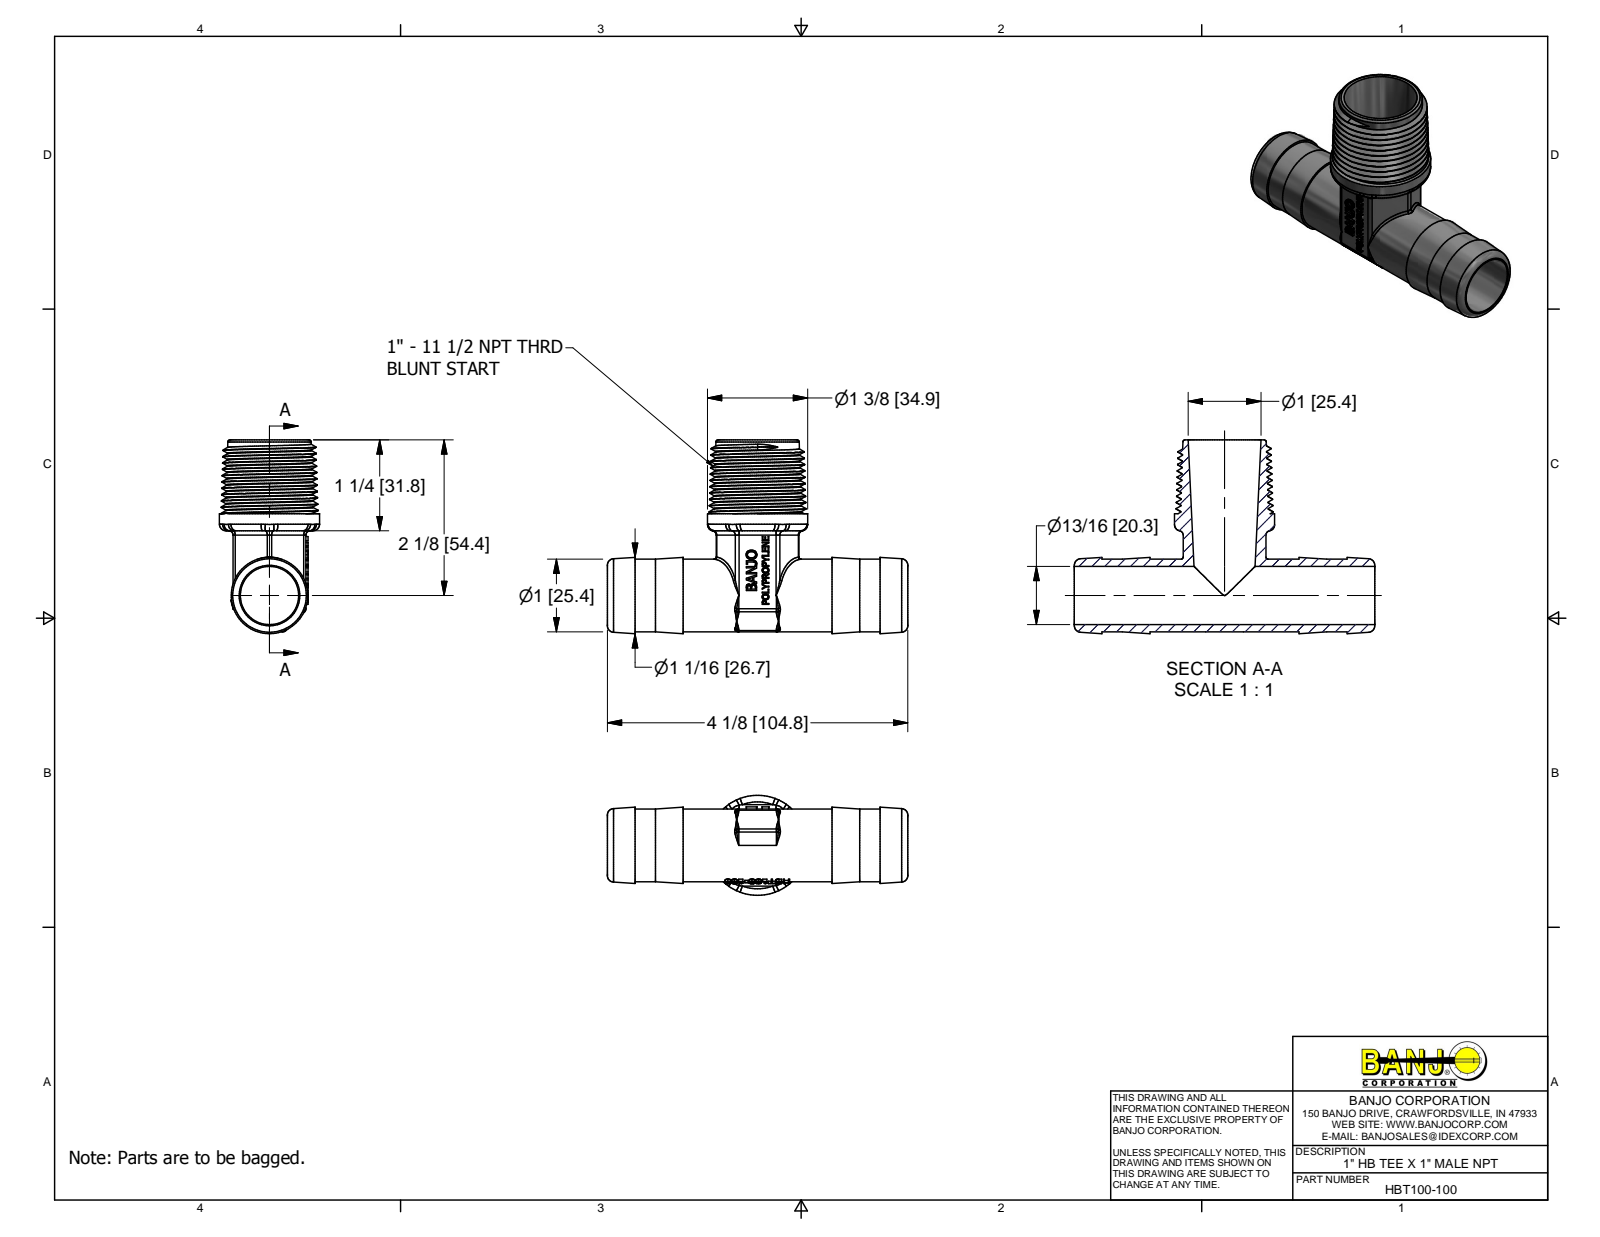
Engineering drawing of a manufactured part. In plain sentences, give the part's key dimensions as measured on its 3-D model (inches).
The part is named "HBT100-100". Its 3-D file was written by "Autodesk Inventor 2012 (AUTOMOTIVE_DESIGN)". It is 1 solid with 529 faces: 242 planar, 43 cylindrical and 244 other. Overall it measures 4.125 by 2.665 by 1.375 inches. Its volume is 1.997 cubic inches and its surface area 38.92 square inches. Round holes: 1 of diameter 0.8. Round bosses or shafts: 1 of diameter 1.375, 1 of diameter 1. Partial cylindrical surfaces (rounded edges, fillets, slot ends): 14 of radius 0.06, 6 of radius 0.03, 1 of radius 0.53. The main face-to-face distances are 1, 0.66, 2.705, 1.017, 1.624, 2.64, 0.38, 1.04, 3.085, 3.745.
